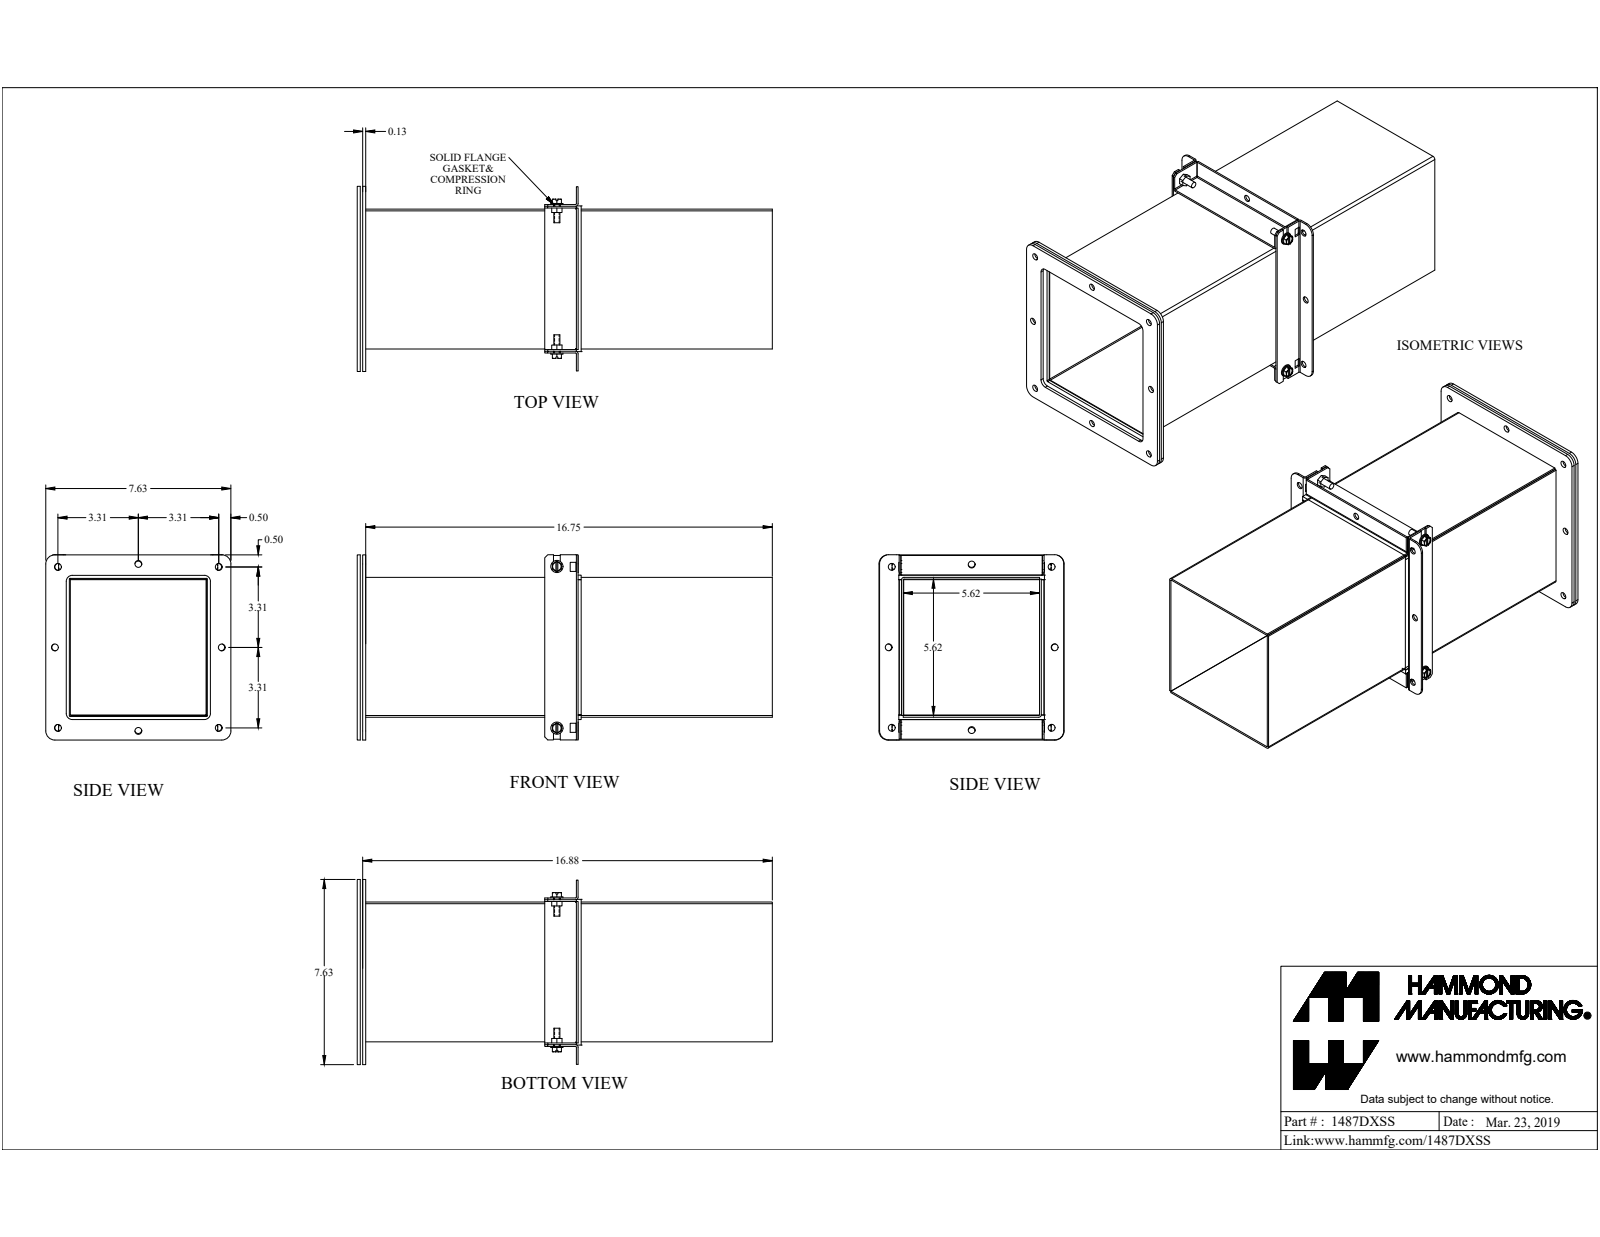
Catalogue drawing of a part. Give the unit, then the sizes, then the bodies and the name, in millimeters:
Units: millimetres
Overall size (bounding box): 443.1 × 193.8 × 193.7
Round holes (diameter × count): ⌀7.1 ×18, ⌀5 ×3, ⌀8.9 ×3, ⌀6.6 ×1
Round bosses / shafts (diameter × count): ⌀12.7 ×3, ⌀6.4 ×3
Partial cylindrical surfaces — rounded edges, fillets, slot ends (radius × count): R0.5 ×26, R0.9 ×10, R2.7 ×10, R9.5 ×8, R0.8 ×4, R6.4 ×4
Main face-to-face distances: 1.8, 1.8, 144.5, 142.6, 144.5, 146.3, 3.2, 5.7, 148.7, 146.9
Hole centre spacings: 84.2, 191, 190.1, 83.7, 123.5, 168.3, 0.4, 0.7
Volume: 671 900 mm³ · Surface area: 678 100 mm²
Bodies: 23 solids, 487 faces (309 planar, 138 cylindrical, 40 other)
Part name (STEP PRODUCT): 1487DXSS
STEP written by: SolidWorks 2019 (CONFIG_CONTROL_DESIGN)
